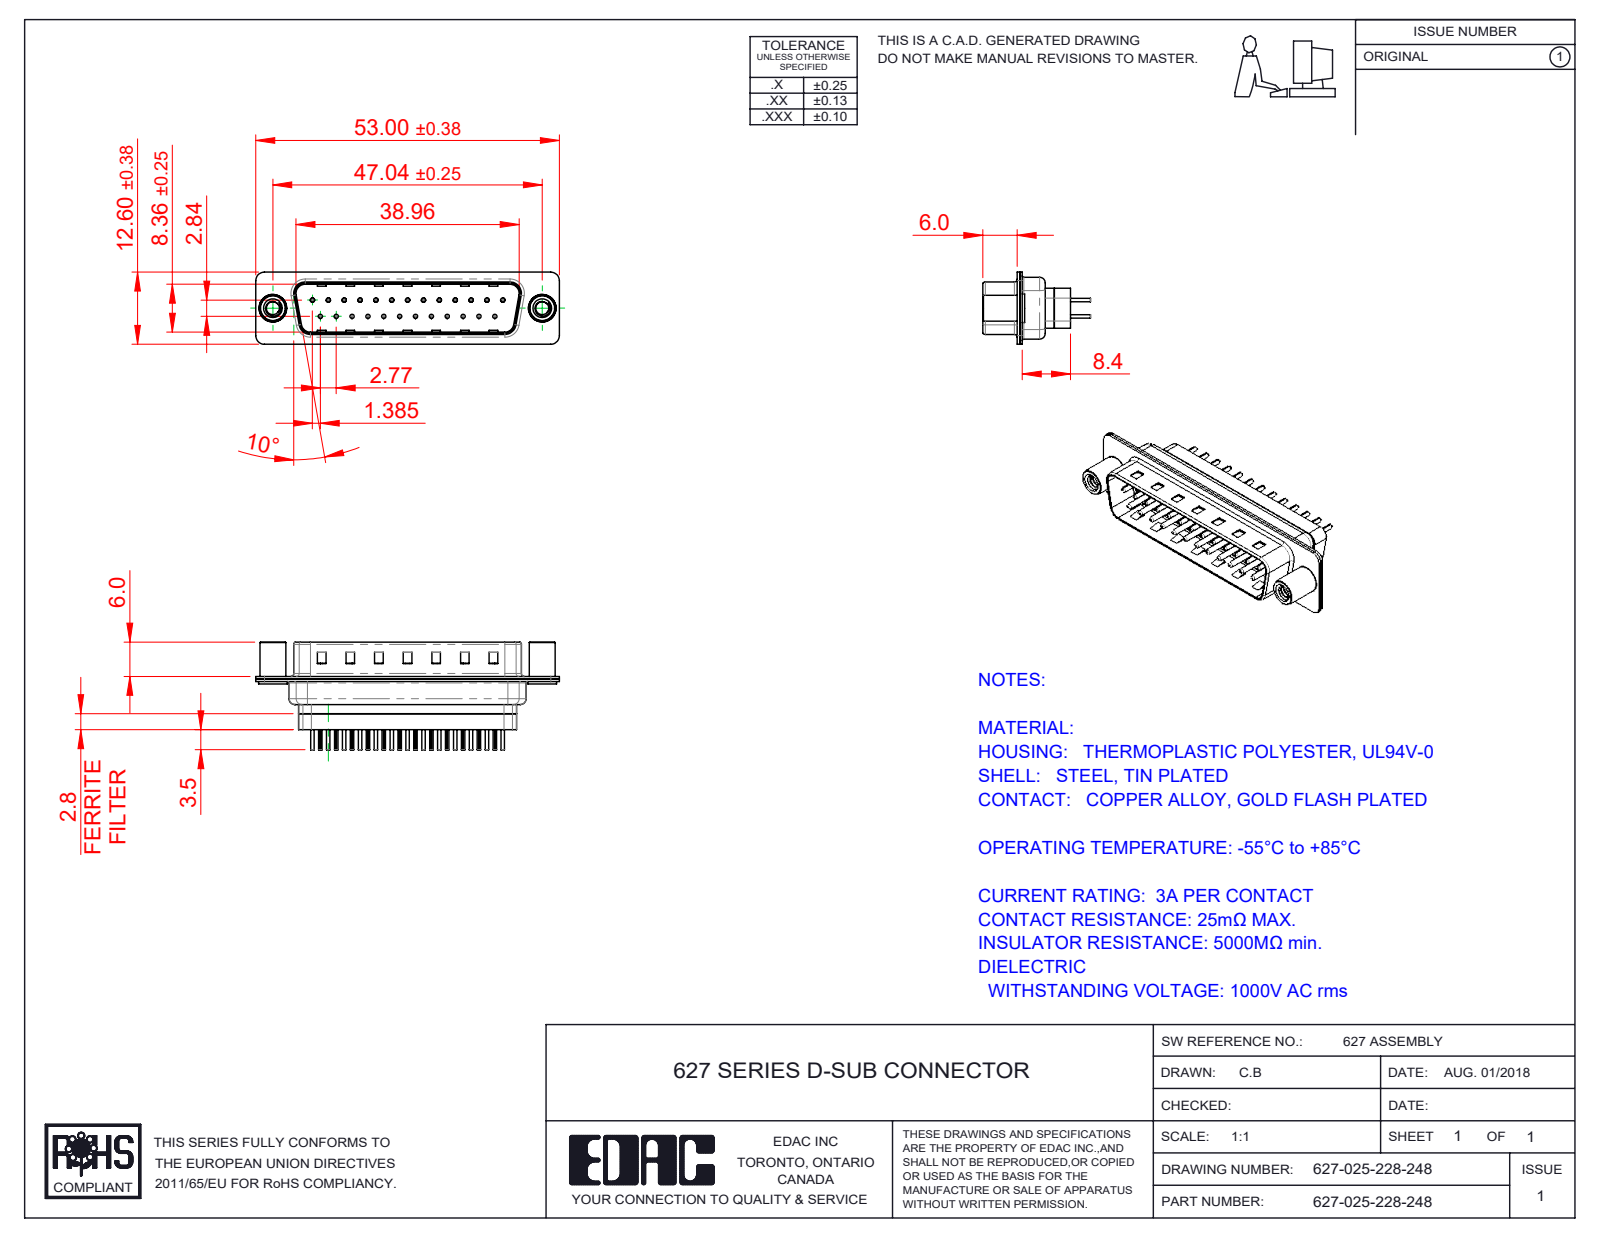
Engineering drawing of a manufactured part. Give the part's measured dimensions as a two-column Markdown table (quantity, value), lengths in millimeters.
| quantity | value |
| --- | --- |
| part name | 627-025-228-048; 627 4-40 Threaded Standoff; 627 Contact Row 2_28L; 627 Housing_25 FF (+3 more) |
| STEP written by | SolidWorks 2020 (CONFIG_CONTROL_DESIGN) |
| units | millimeters |
| bodies | 31 solids, 2921 faces (779 planar, 1145 cylindrical, 997 other) |
| overall size | 53 × 18.8 × 12.6 |
| volume | 3 341 mm³ |
| surface area | 9 119 mm² |
| round holes (diameter × count) | 0.2 × 25, 0.35 × 25, 1.1 × 25, 1.6 × 25, 2.26 × 2, 4 × 2, 4.8 × 2 |
| round bosses / shafts (diameter × count) | 2 × 25, 1.5 × 25, 0.75 × 25, 0.6 × 25, 5 × 2, 4.9 × 2, 4.5 × 2 |
| partial cylindrical surfaces (radius × count) | 0.1 × 50, 1.5 × 16, 2 × 12, 0.5 × 8, 1.6 × 8, 0.25 × 4, 0.6 × 4, 0.65 × 4 |
| main face-to-face distances | 0.4, 0.45, 6.05, 0.82, 9.58, 8.4, 0.9, 1.5, 0.68, 7.68 |
| hole center spacings | 3.16, 2.77, 5.54, 8.31, 11.08, 13.85, 5.04, 7.49 |
